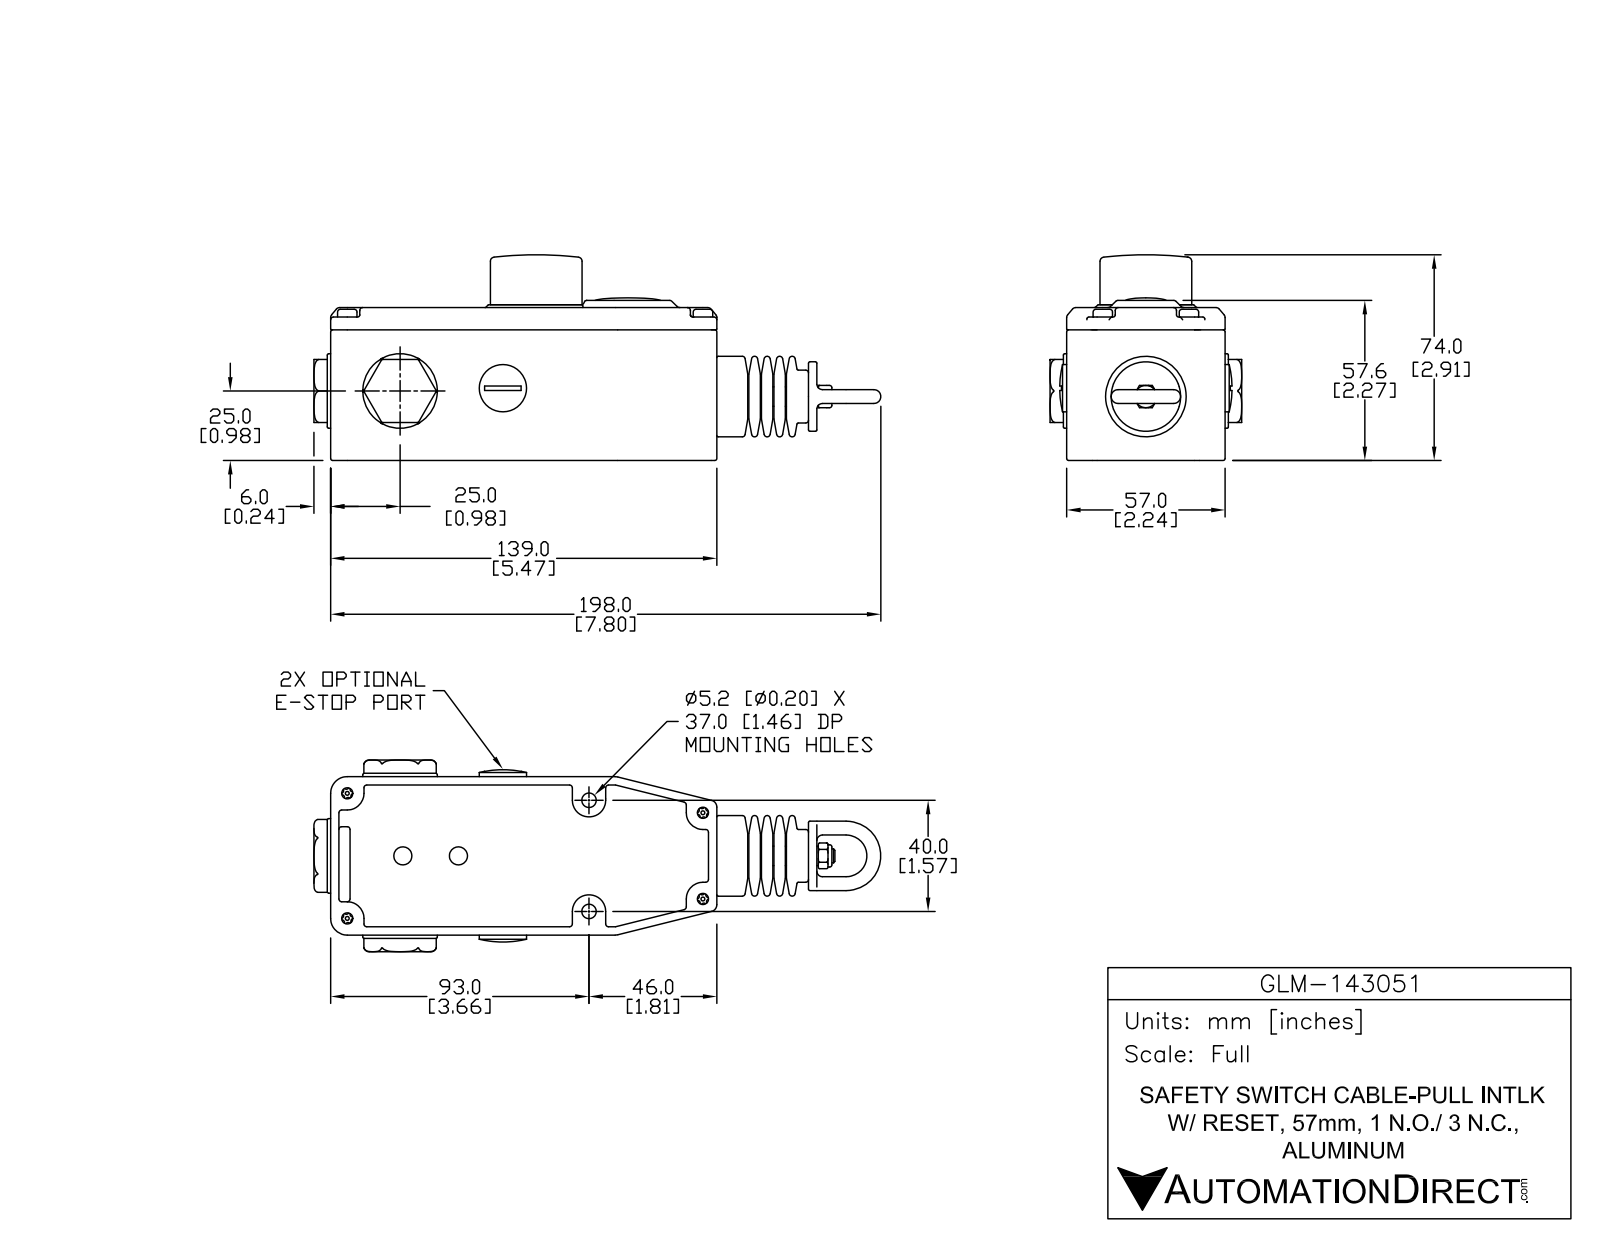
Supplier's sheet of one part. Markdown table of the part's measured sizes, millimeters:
| quantity | value |
| --- | --- |
| part name | GLM-143051 |
| STEP written by | SolidWorks 2013 (AUTOMOTIVE_DESIGN) |
| units | millimeters |
| bodies | 1 solid, 407 faces (126 planar, 146 cylindrical, 135 other) |
| overall size | 193.26 × 75 × 69.6 |
| volume | 449 421 mm³ |
| surface area | 46 731 mm² |
| round holes (diameter × count) | 4 × 4, 5.2 × 2 |
| round bosses / shafts (diameter × count) | 7 × 5, 26.8 × 2, 5 × 2, 35.2 × 1, 33 × 1, 29 × 1, 25 × 1, 19 × 1 |
| partial cylindrical surfaces (radius × count) | 0.5 × 30, 0.16 × 19, 0.25 × 12, 1 × 8, 4.5 × 2, 4.57 × 2, 7 × 2, 13 × 2 |
| main face-to-face distances | 54.68, 57, 55, 0.32, 139, 6.3, 63.3, 145, 6, 3 |
| hole center spacings | 41.25, 54.23, 87.04, 96.83, 128.19, 133.52, 31, 40 |
